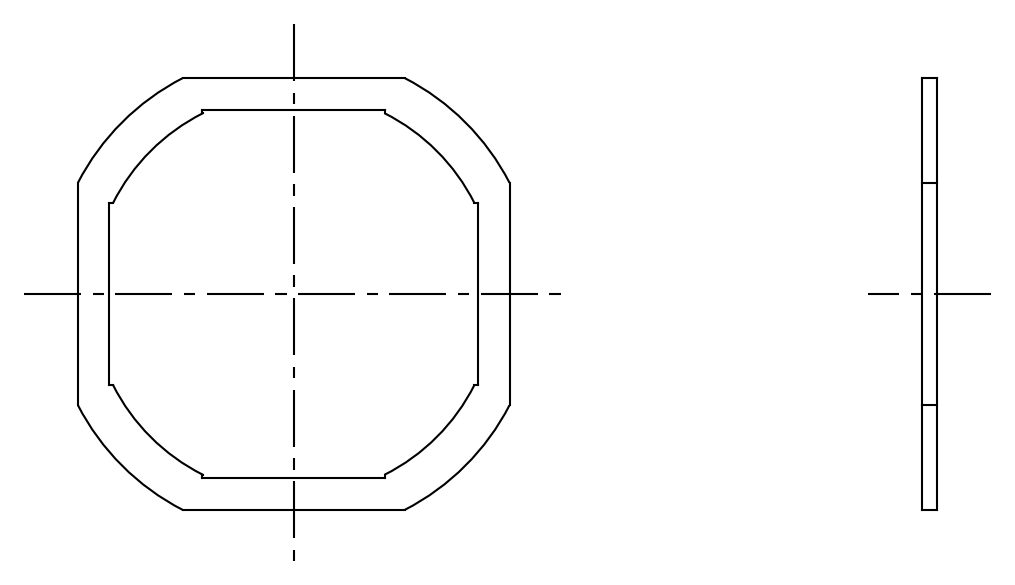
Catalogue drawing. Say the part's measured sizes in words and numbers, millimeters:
The part is named "packing". Its 3-D file was written by "CADfix (AUTOMOTIVE_DESIGN)". It is 1 solid with 30 faces: 0 planar, 0 cylindrical and 30 other. Overall it measures 24 by 24 by 0.8 millimeters. Its volume is 120 cubic millimeters and its surface area 422 square millimeters.
